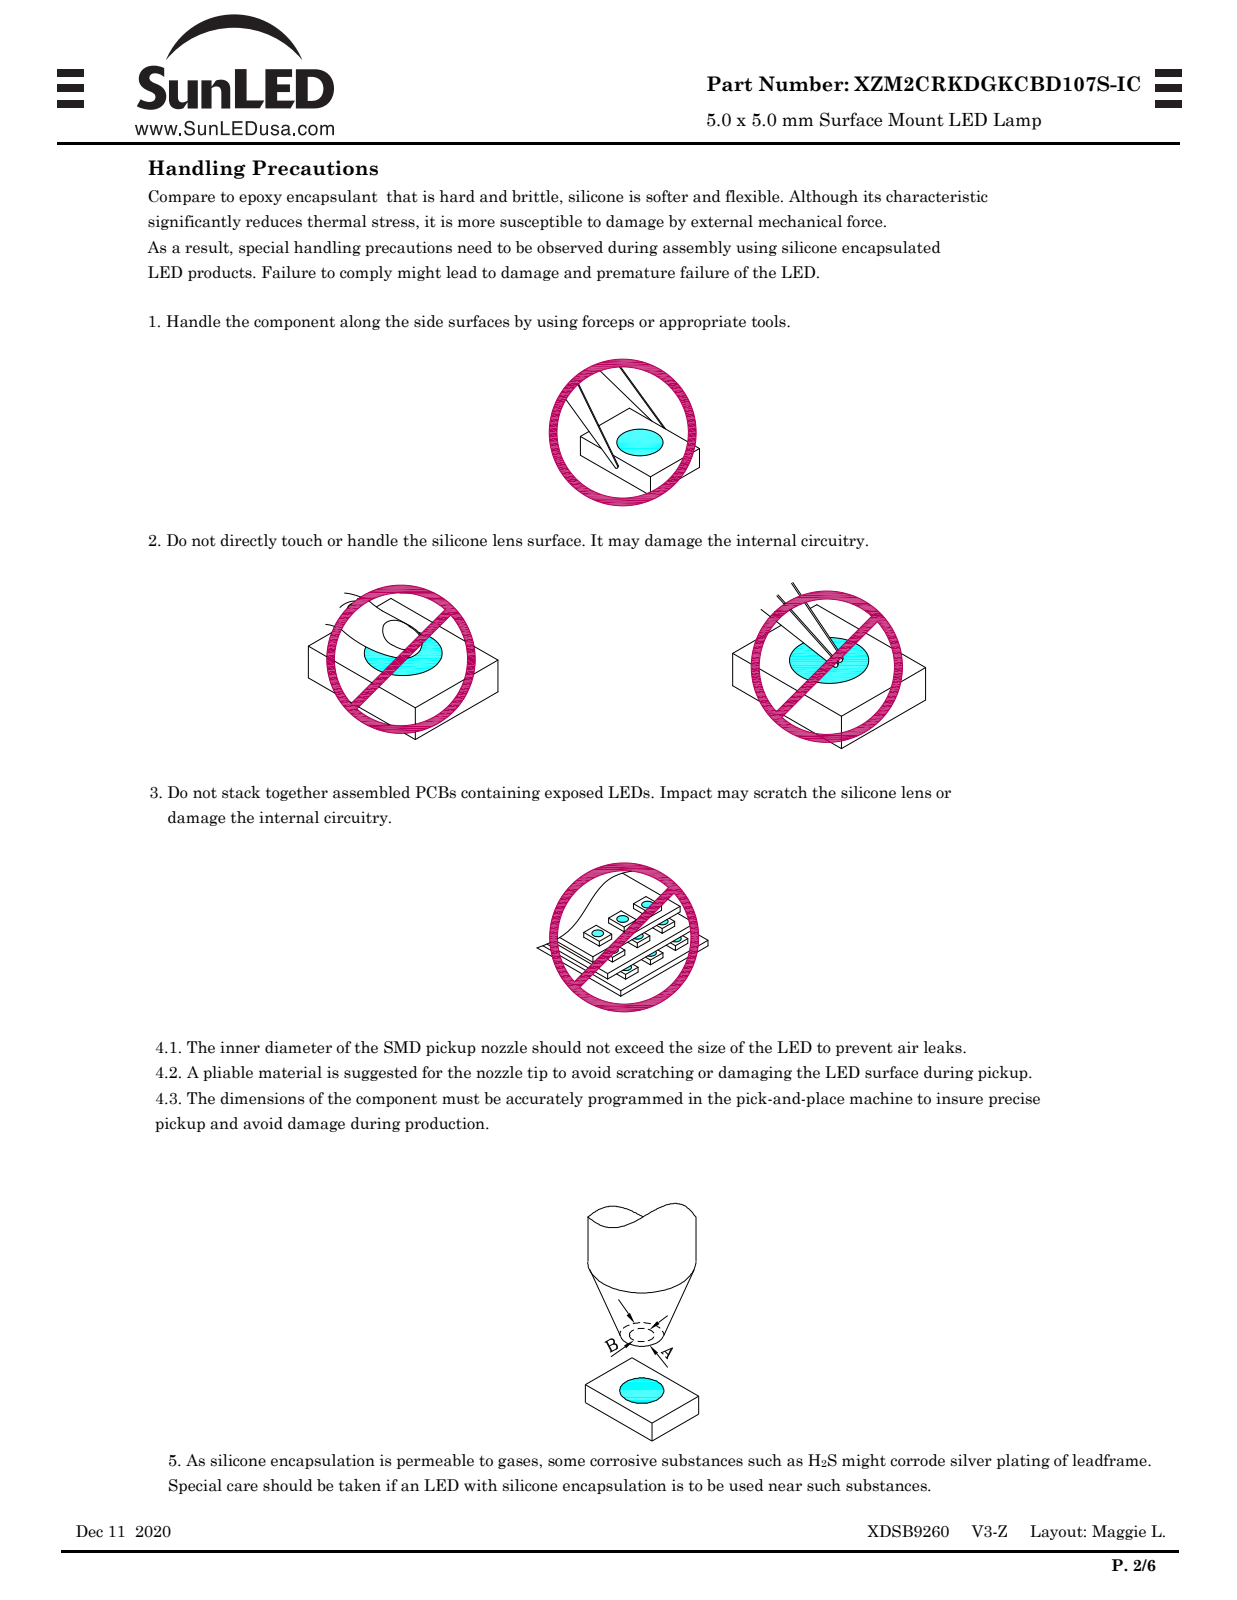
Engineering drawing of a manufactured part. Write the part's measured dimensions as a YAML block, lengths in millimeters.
part_name: "XZM2CRKDGKCBD107S-IC"
step_written_by: "SolidWorks 2014 (AUTOMOTIVE_DESIGN)"
units: millimeters
bodies: {solids: 14, faces: 141, planar: 116, cylindrical: 19, other: 6}
overall_size: [5.4, 5, 1.6]
volume: 40
surface_area: 163
round_bosses_or_shafts:
  - {diameter: 3.4, count: 1}
partial_cylinders:
  - {radius: 0.15, count: 4}
face_to_face_distances: [0.8, 1.6, 0.6, 5, 0.58, 1.38, 0.82, 0.78, 0.77, 0.55]
